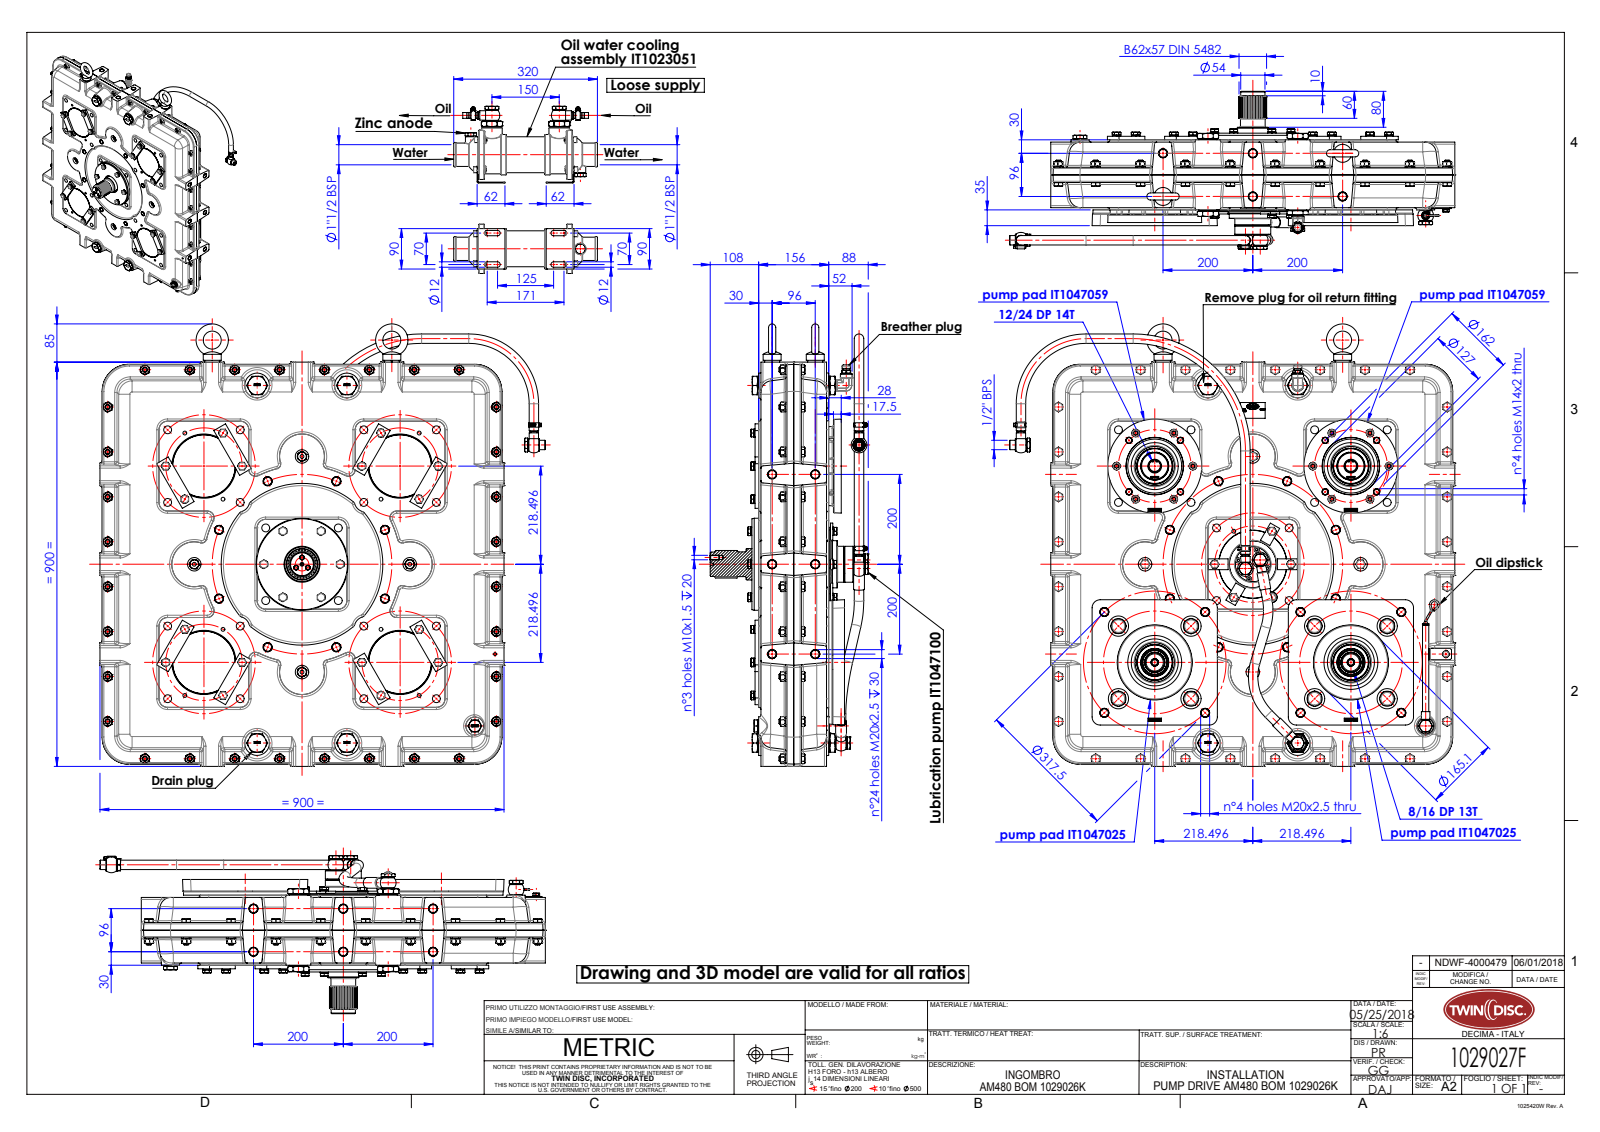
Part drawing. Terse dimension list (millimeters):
name: ITam480-002_rev00-installation; ITB01100000_rev01-installation; 1029027F; IT1023051_rev00-installation (+8 more)
written by: SolidWorks 2015 (AUTOMOTIVE_DESIGN)
unit: mm
bodies: 302 solids, 14406 faces (6536 planar, 4436 cylindrical, 3434 other)
size: 1535.5 × 1221 × 991.95
volume: 106 900 000 mm³; area: 7 551 000 mm²
holes: 49× ⌀13, 48× ⌀17.5, 36× ⌀10.3, 36× ⌀12.2, 33× ⌀8.5, 32× ⌀11, 26× ⌀20, 22× ⌀10.2, 21× ⌀21, 15× ⌀8, 13× ⌀17, 10× ⌀20.2
bosses: 41× ⌀18, 36× ⌀21.1, 36× ⌀12, 33× ⌀10, 22× ⌀18.1, 22× ⌀16.2, 14× ⌀16, 12× ⌀20
rounds: 346× R0.35, 288× R38.33, 176× R5, 58× R0.45, 58× R29.02, 58× R29.53, 53× R1, 36× R10.97
face distances: 73, 151, 5, 78, 146, 156, 17, 7, 40, 61
hole spacings: 200, 100, 400, 300, 221.85, 282.85, 369.56, 500
